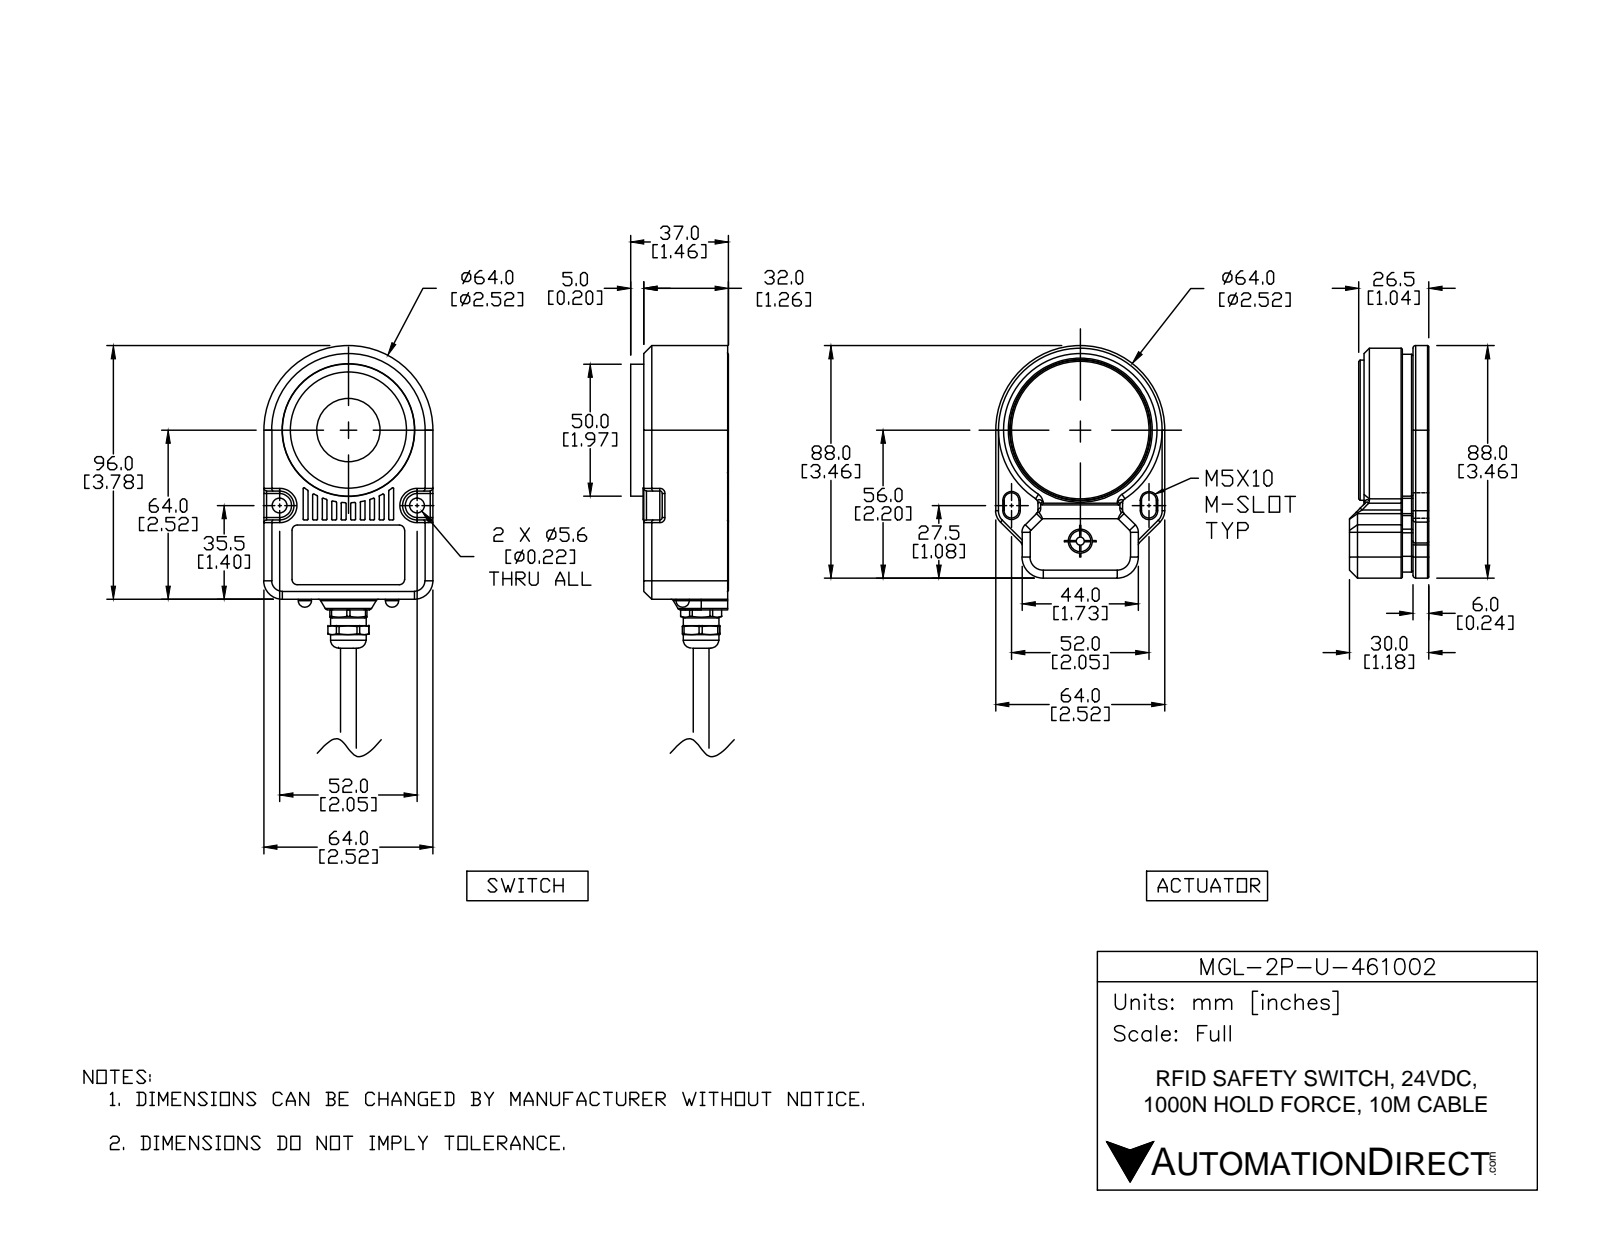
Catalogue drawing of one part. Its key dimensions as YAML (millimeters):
part_name: "MGL-2P-U-461002; MGL-2P-U-461002_1; MGL-2P-U-461002_2"
step_written_by: "SolidWorks 2017 (AUTOMOTIVE_DESIGN)"
units: millimeters
bodies: {solids: 17, faces: 1585, planar: 431, cylindrical: 674, other: 480}
overall_size: [196, 64.5, 64]
volume: 194400
surface_area: 99680
round_holes:
  - {diameter: 4, count: 6}
  - {diameter: 8, count: 6}
  - {diameter: 2.4, count: 4}
  - {diameter: 5, count: 4}
  - {diameter: 2, count: 2}
  - {diameter: 3.3, count: 2}
  - {diameter: 5.6, count: 2}
  - {diameter: 9, count: 2}
  - {diameter: 10.5, count: 2}
  - {diameter: 17, count: 2}
  - {diameter: 6.4, count: 1}
  - {diameter: 6.5, count: 1}
round_bosses_or_shafts:
  - {diameter: 0.5, count: 4}
  - {diameter: 2, count: 3}
  - {diameter: 12, count: 2}
  - {diameter: 6, count: 2}
  - {diameter: 5.8, count: 2}
  - {diameter: 5.4, count: 2}
  - {diameter: 3.7, count: 2}
  - {diameter: 62, count: 1}
partial_cylinders:
  - {radius: 0.5, count: 180}
  - {radius: 1, count: 60}
  - {radius: 0.3, count: 39}
  - {radius: 2, count: 20}
  - {radius: 0.6, count: 7}
  - {radius: 4, count: 6}
  - {radius: 6, count: 5}
  - {radius: 8, count: 5}
face_to_face_distances: [2.5, 6, 58.5, 10.5, 16.5, 64.5, 3, 61.5, 10, 8]
hole_center_spacings: [17.9, 19.5, 27.6, 17, 26, 29.4, 4.4, 8.8]
